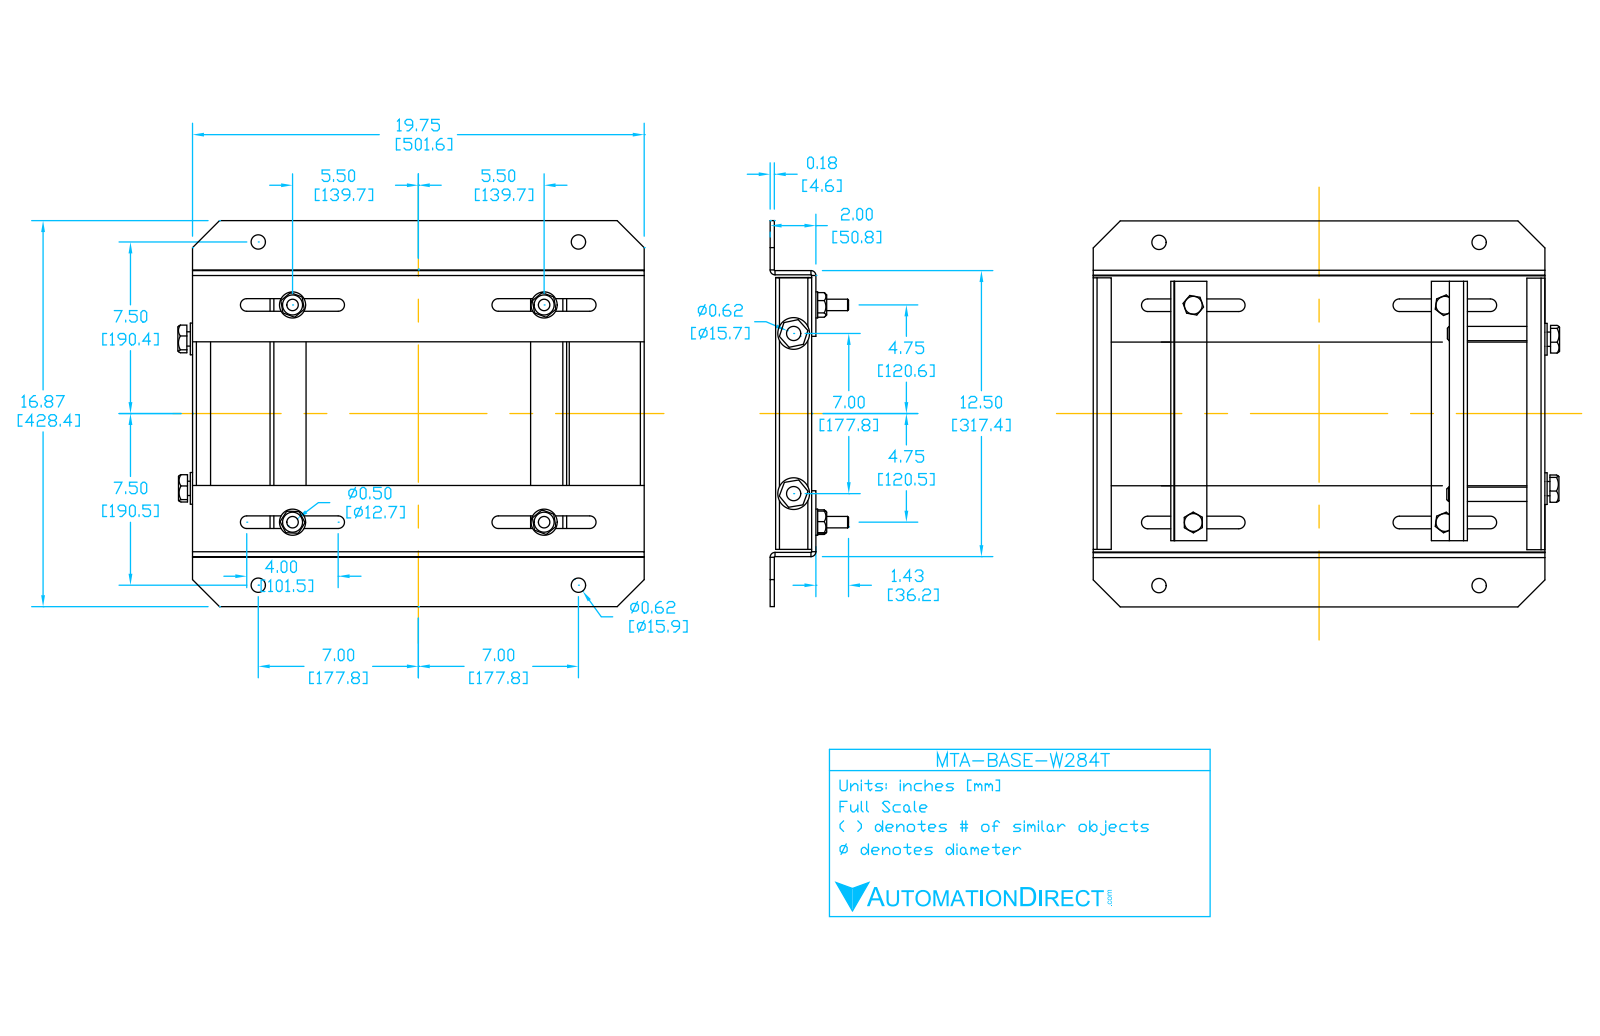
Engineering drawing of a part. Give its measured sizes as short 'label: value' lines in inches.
name: W284T
written by: SolidWorks 2017 (AUTOMOTIVE_DESIGN)
unit: in
bodies: 26 solids, 394 faces (224 planar, 106 cylindrical, 64 other)
size: 20.321 × 16.875 × 3.697
volume: 75.48 in³; area: 940.1 in²
holes: 4× ⌀0.5, 4× ⌀0.504, 4× ⌀0.531, 4× ⌀0.625, 2× ⌀0.625, 2× ⌀0.65, 2× ⌀0.748
bosses: 4× ⌀1.142, 2× ⌀1.386, 1× ⌀0.625
rounds: 11× R0.029, 8× R0.289, 4× R0.167, 4× R0.214, 3× R0.147
face distances: 0.185, 1.815, 2, 1.63, 0.118, 12.315, 0.138, 1.697, 1.457, 0.303
hole spacings: 4, 9.5, 11.43, 11.844, 14, 15, 15.183, 20.518
